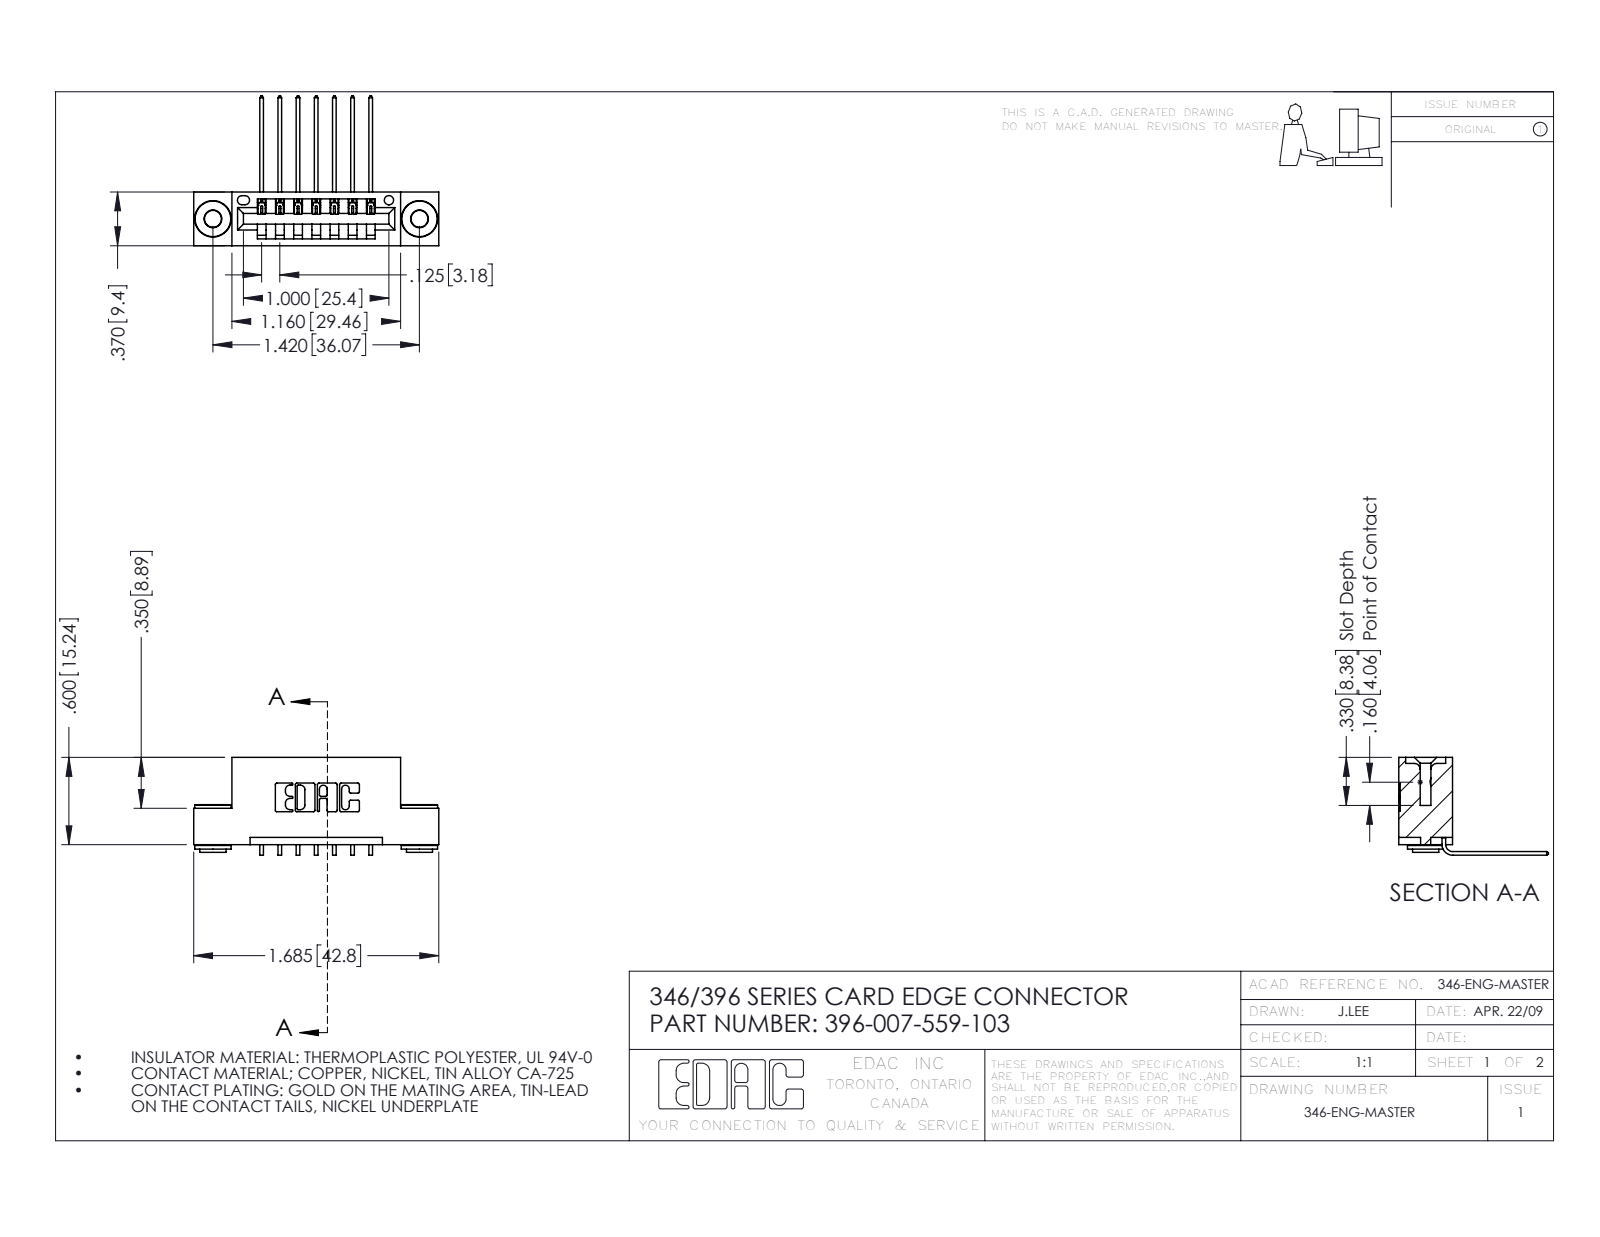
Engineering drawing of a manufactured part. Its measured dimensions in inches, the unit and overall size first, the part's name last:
Units: inches
Overall size (bounding box): 1.685 × 1.03 × 0.673
Round holes (diameter × count): ⌀0.116 ×2, ⌀0.156 ×2, ⌀0.064 ×1
Round bosses / shafts (diameter × count): ⌀0.25 ×2, ⌀0.18 ×2, ⌀0.136 ×2
Partial cylindrical surfaces — rounded edges, fillets, slot ends (radius × count): R0.01 ×22, R0.006 ×14, R0.007 ×6, R0.031 ×6, R0.026 ×3, R0.031 ×2, R0.04 ×2, R0.014 ×1
Main face-to-face distances: 0.25, 0.37, 0.048, 0.322, 0.025, 0.072, 0.298, 0.148, 0.222, 0.1
Hole centre spacings: 0.246, 1.217, 1.42
Volume: 0.238 in³ · Surface area: 7.522 in²
Bodies: 10 solids, 580 faces (380 planar, 192 cylindrical, 8 other)
Part name (STEP PRODUCT): 345-292-001_558 559 Tail - 1; 345-250-002_345-250-002-102; 396-007-559-103; 346 Part_Flush Mounting Lugs - 0.156 Dia-TH
STEP written by: SolidWorks 2016 (CONFIG_CONTROL_DESIGN)
